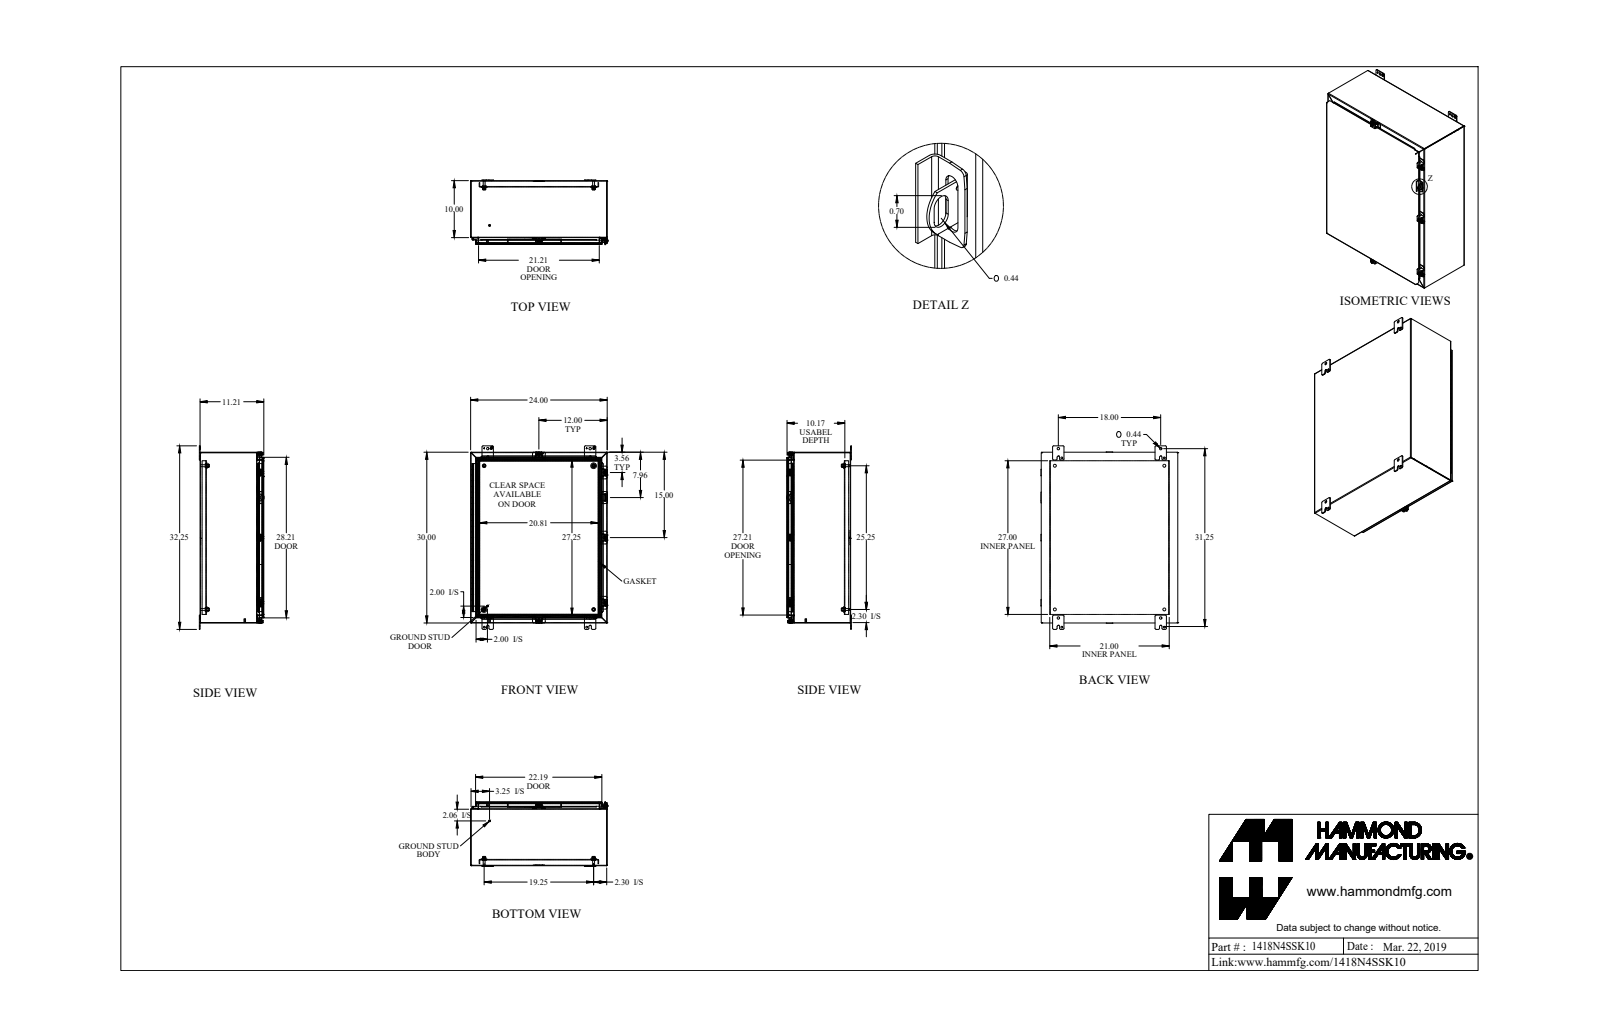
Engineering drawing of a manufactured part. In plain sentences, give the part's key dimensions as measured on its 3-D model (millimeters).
The part is named "1418N4SSK10_Default". Its 3-D file was written by "SolidWorks 2019 (CONFIG_CONTROL_DESIGN)". It is 43 solids with 1687 faces: 1037 planar, 556 cylindrical and 94 other. Overall it measures 819.2 by 611.2 by 288.9 millimeters. Its volume is 4 485 000 cubic millimeters and its surface area 4 648 000 square millimeters. Round holes: 5 of diameter 5.4, 5 of diameter 6.7, 5 of diameter 9.5, 4 of diameter 8, 4 of diameter 11.1, 4 of diameter 12.7, 2 of diameter 7.8, 2 of diameter 11.3, 1 of diameter 3.2, 1 of diameter 4.7. Round bosses or shafts: 5 of diameter 12.7, 5 of diameter 9.9, 5 of diameter 6.2, 4 of diameter 16.5, 4 of diameter 9.5, 4 of diameter 8.4, 2 of diameter 25.4, 2 of diameter 8. Partial cylindrical surfaces (rounded edges, fillets, slot ends): 27 of radius 1.2, 27 of radius 3.6, 26 of radius 4.8, 24 of radius 0.9, 24 of radius 2.7, 24 of radius 6.4, 10 of radius 3.2, 10 of radius 3.6. The main face-to-face distances are 1.8, 1.8, 282.9, 281.1, 282.9, 284.7, 2.4, 23.8, 607.8, 25.6. The hole center spacings are 737.1, 44.1, 250.4, 457.2, 489, 755.7, 883.2, 77.9.
